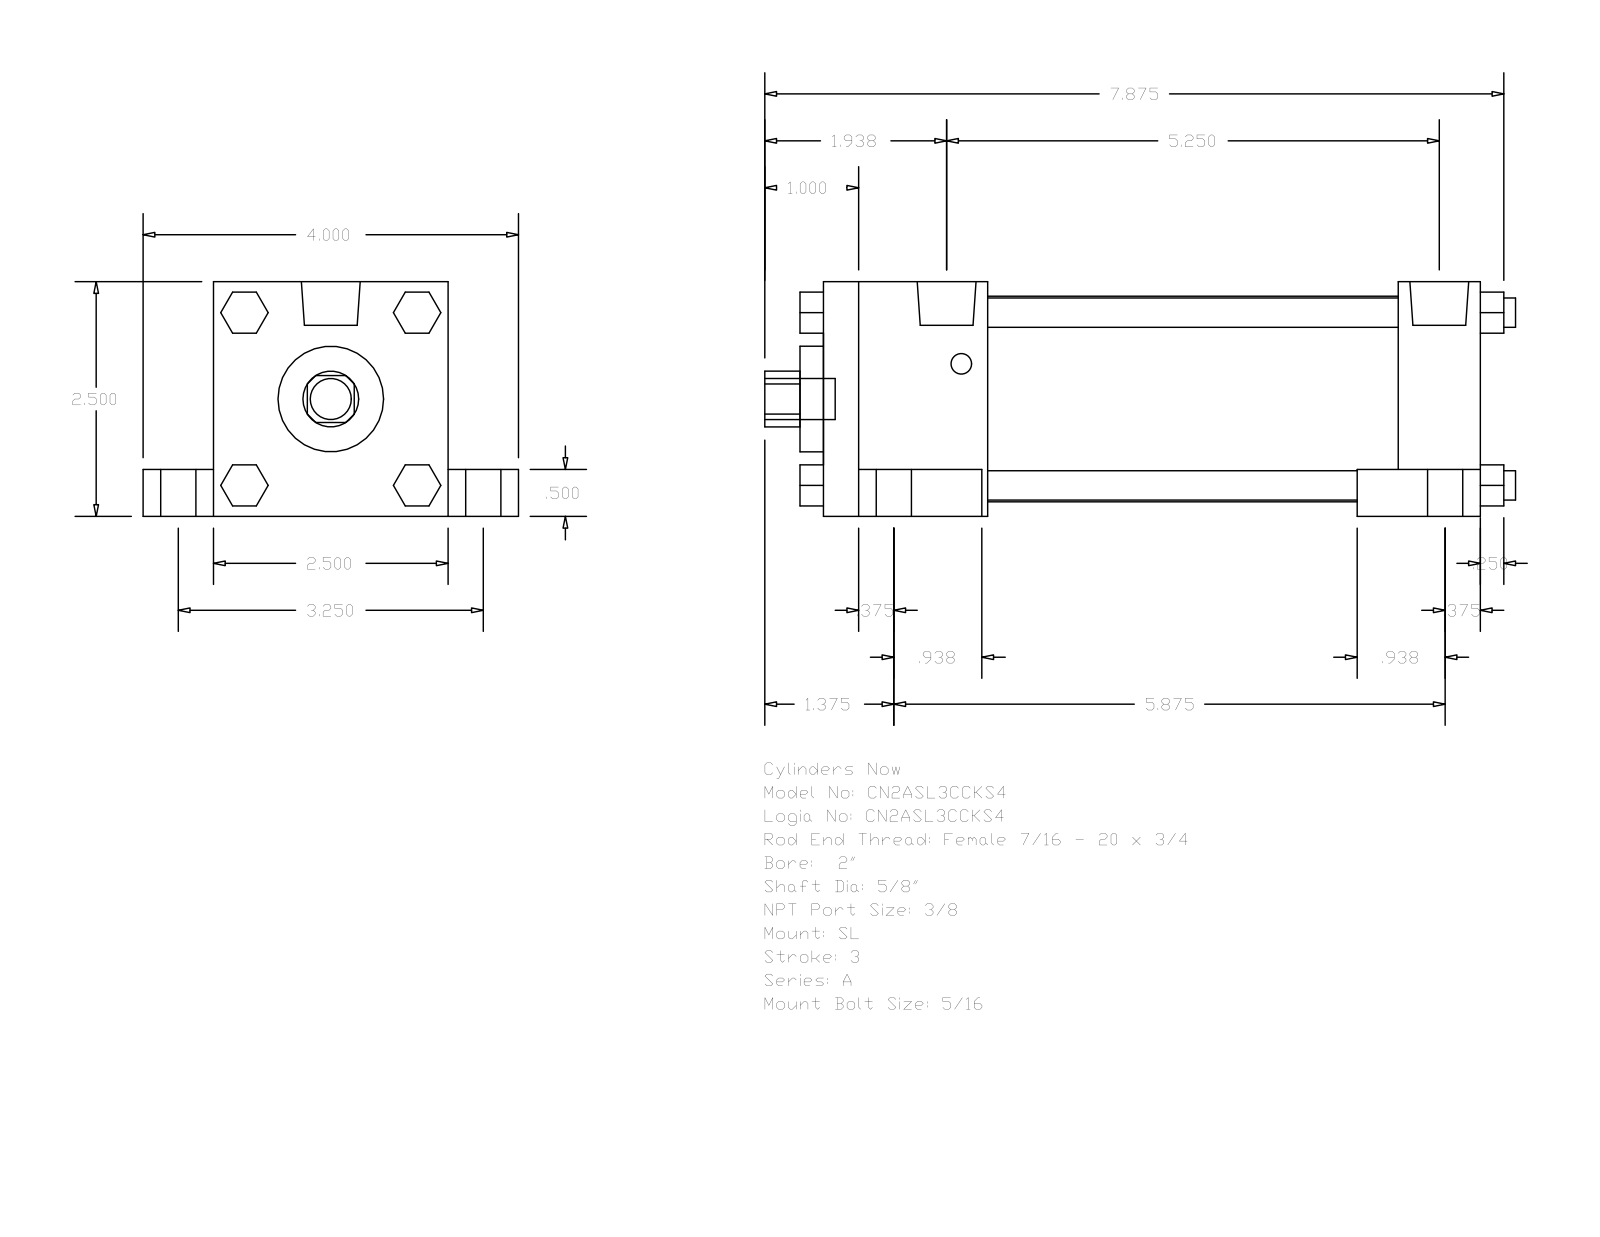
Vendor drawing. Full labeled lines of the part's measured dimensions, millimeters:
Part name (STEP PRODUCT): A_SL__0200_0.625
STEP written by: GSSL Pune (CONFIG_CONTROL_DESIGN)
Units: millimetres
Bodies: 0 solids, 148 faces (112 planar, 36 cylindrical, 0 other)
Overall size (bounding box): 203.2 × 101.6 × 63.5
Round holes (diameter × count): ⌀15.88 ×1, ⌀28.57 ×1, ⌀55.63 ×1
Round bosses / shafts (diameter × count): ⌀15.88 ×4, ⌀9.53 ×4, ⌀7.94 ×4, ⌀5.56 ×4, ⌀15.93 ×2, ⌀11.11 ×1
Partial cylindrical surfaces — rounded edges, fillets, slot ends (radius × count): R7.54 ×1
Main face-to-face distances: 63.5, 177.8, 50.8, 12.7, 19.05, 82.55, 44.45, 133.35, 155.57, 111.12
